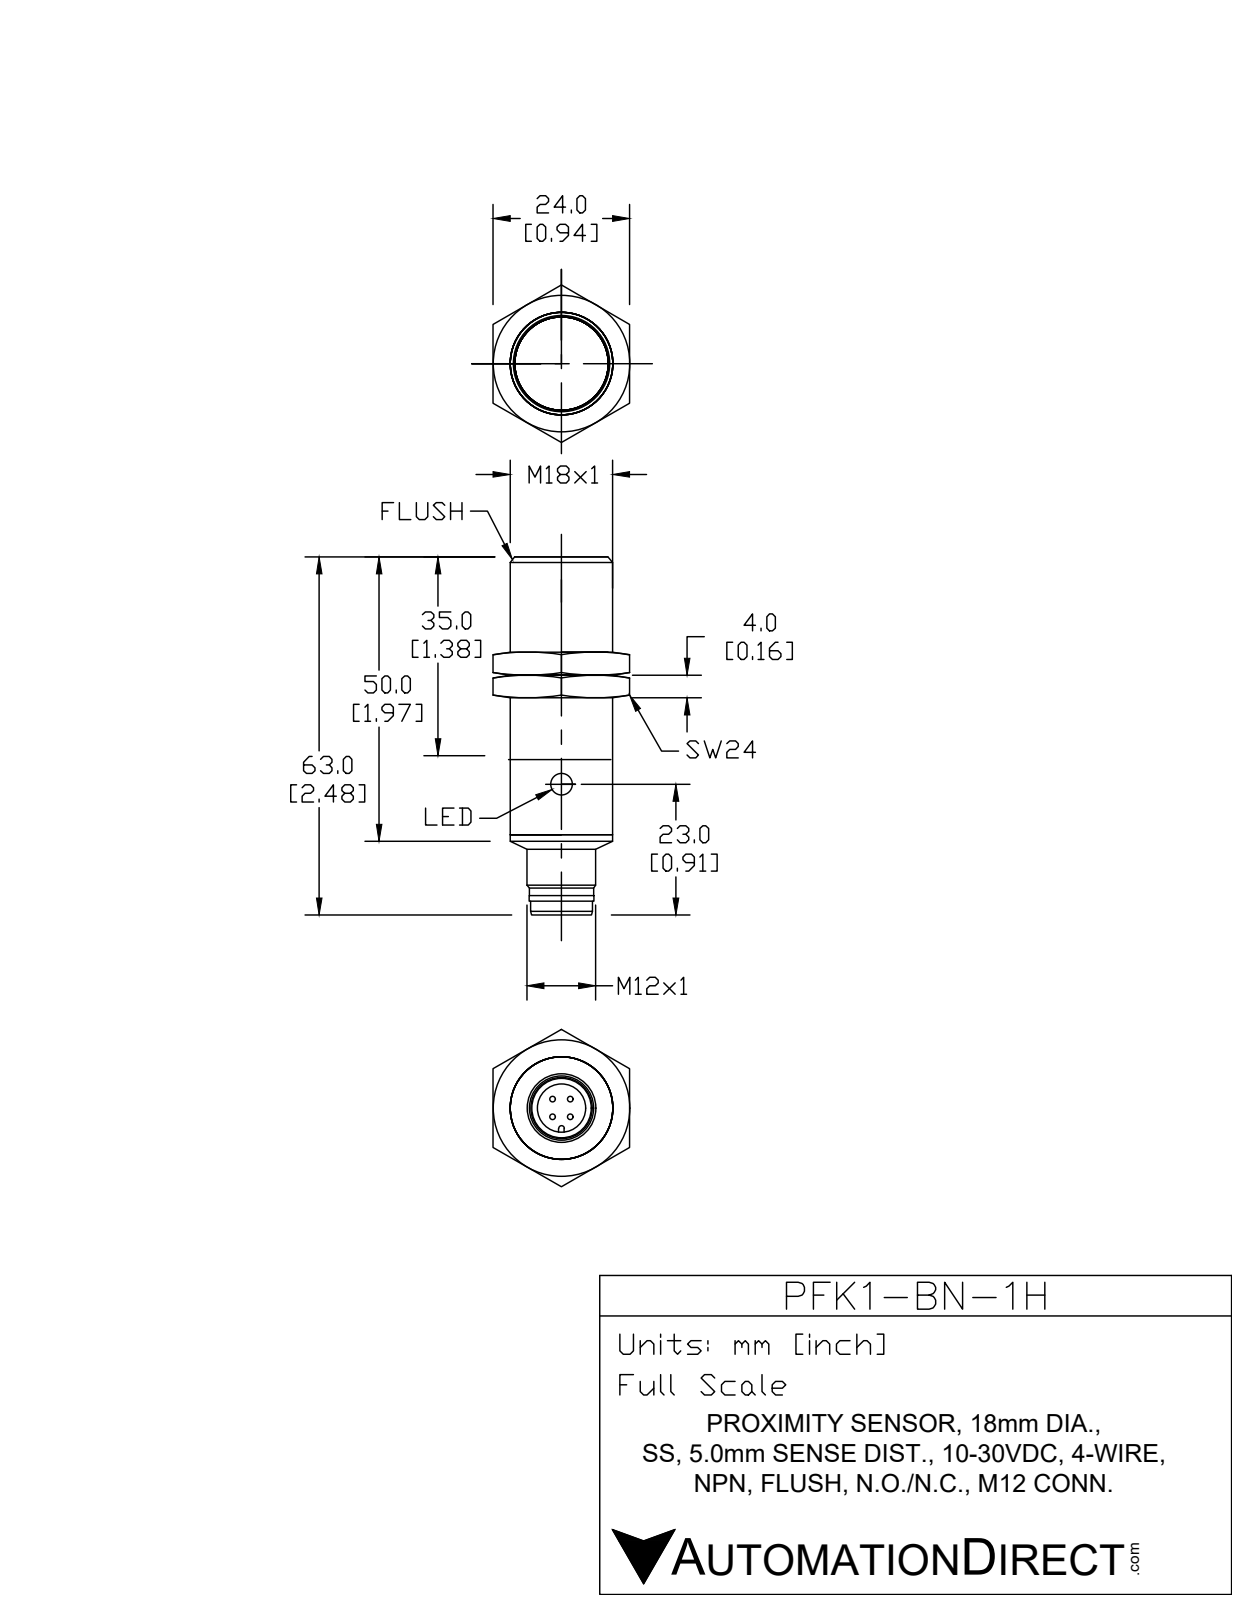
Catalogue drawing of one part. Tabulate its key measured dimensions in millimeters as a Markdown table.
| quantity | value |
| --- | --- |
| part name | PFK1-BN-1H |
| STEP written by | SolidWorks 2017 (AUTOMOTIVE_DESIGN) |
| units | millimeters |
| bodies | 4 solids, 69 faces (12 planar, 35 cylindrical, 22 other) |
| overall size | 63.1 × 18 × 18 |
| volume | 13 700 mm³ |
| surface area | 6 632 mm² |
| round holes (diameter × count) | 4 × 1, 8.4 × 1, 8.5 × 1, 9.5 × 1, 15.8 × 1 |
| round bosses / shafts (diameter × count) | 1 × 4, 18 × 1, 12 × 1, 10.5 × 1, 9.4 × 1 |
| partial cylindrical surfaces (radius × count) | 0.6 × 1, 8.3 × 1 |
| main face-to-face distances | 39.1, 10, 49.1, 53, 43, 3.9, 54.2, 44.2, 5.1, 1.2 |
